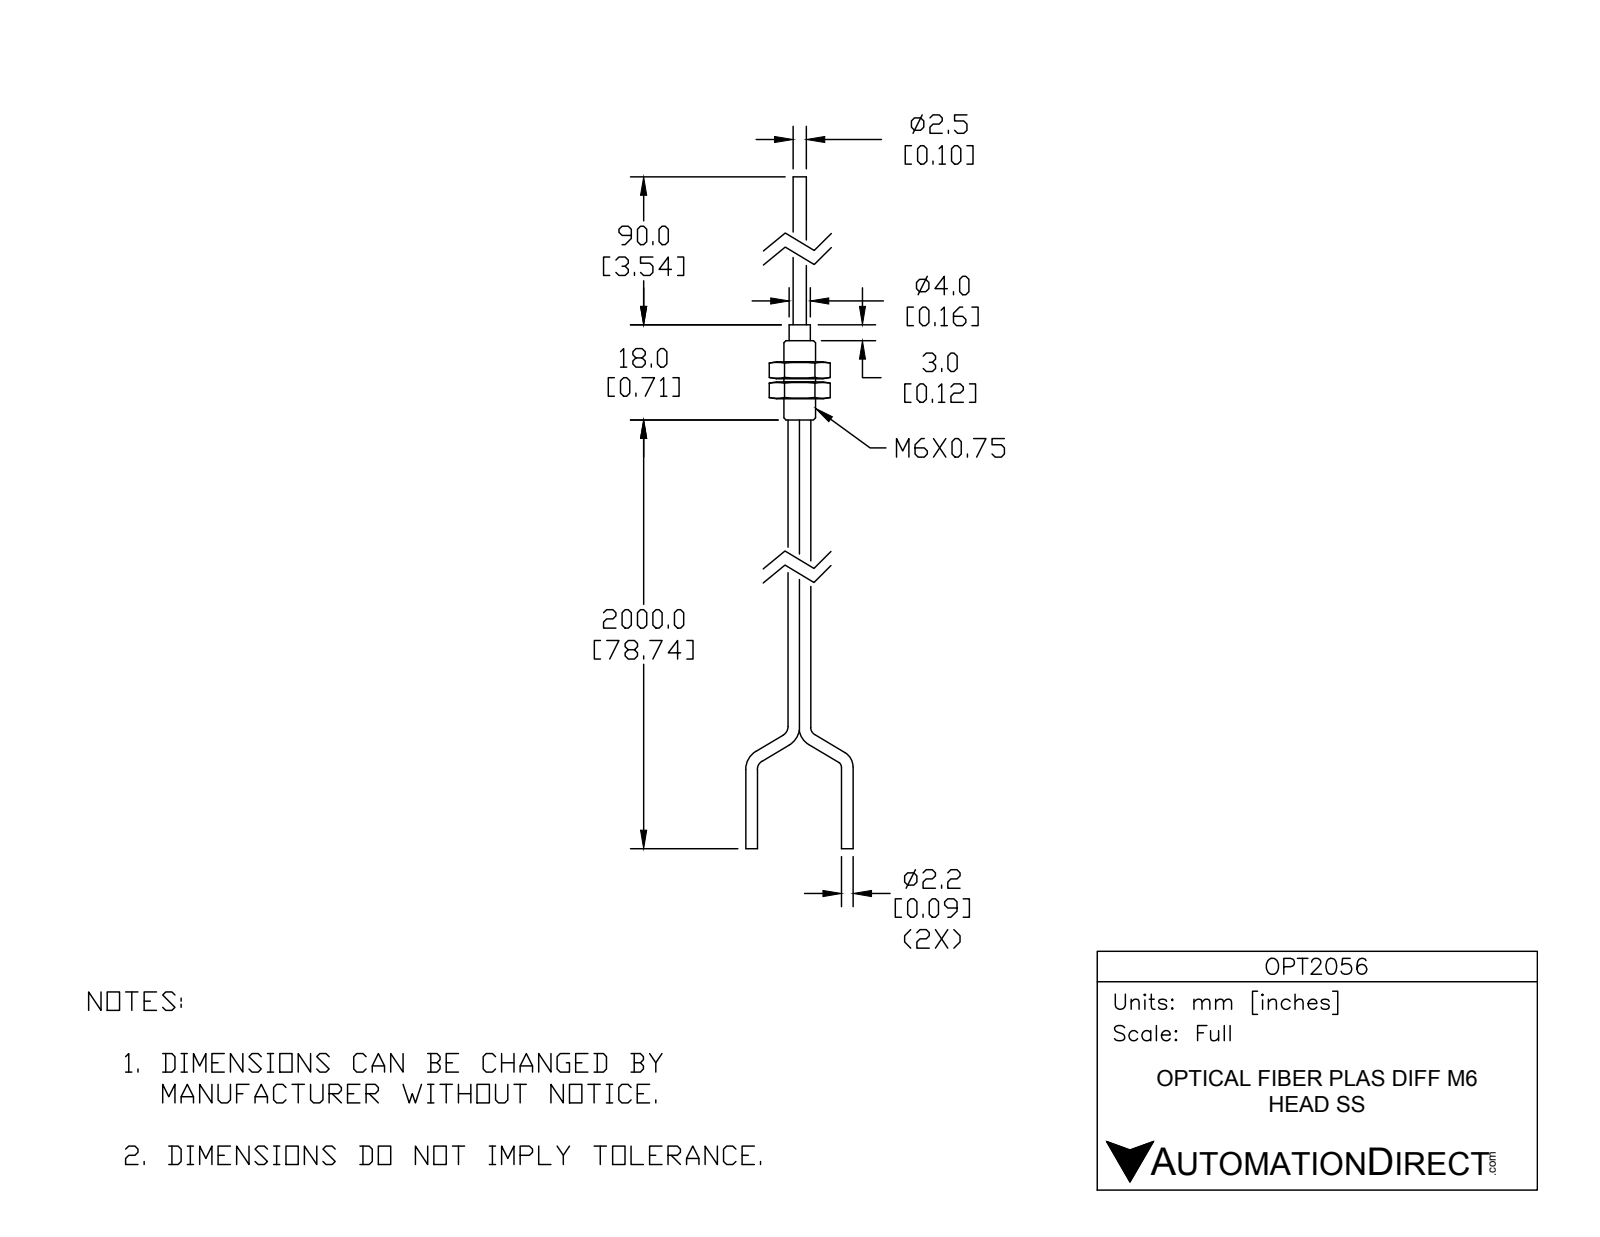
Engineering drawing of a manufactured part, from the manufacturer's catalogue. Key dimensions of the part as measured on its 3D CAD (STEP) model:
Part name (STEP PRODUCT): OPT2056
STEP written by: SolidWorks 2014 (AUTOMOTIVE_DESIGN)
Units: inches
Bodies: 5 solids, 78 faces (30 planar, 28 cylindrical, 20 other)
Overall size (bounding box): 5.004 × 0.799 × 0.394
Volume: 0.091 in³ · Surface area: 2.883 in²
Round bosses / shafts (diameter × count): ⌀0.087 ×6, ⌀0.236 ×1, ⌀0.157 ×1, ⌀0.098 ×1
Main face-to-face distances: 0.394, 0.126, 0.15, 0.276, 0.024, 0.157, 0.283, 0.307, 0.433, 0.591
